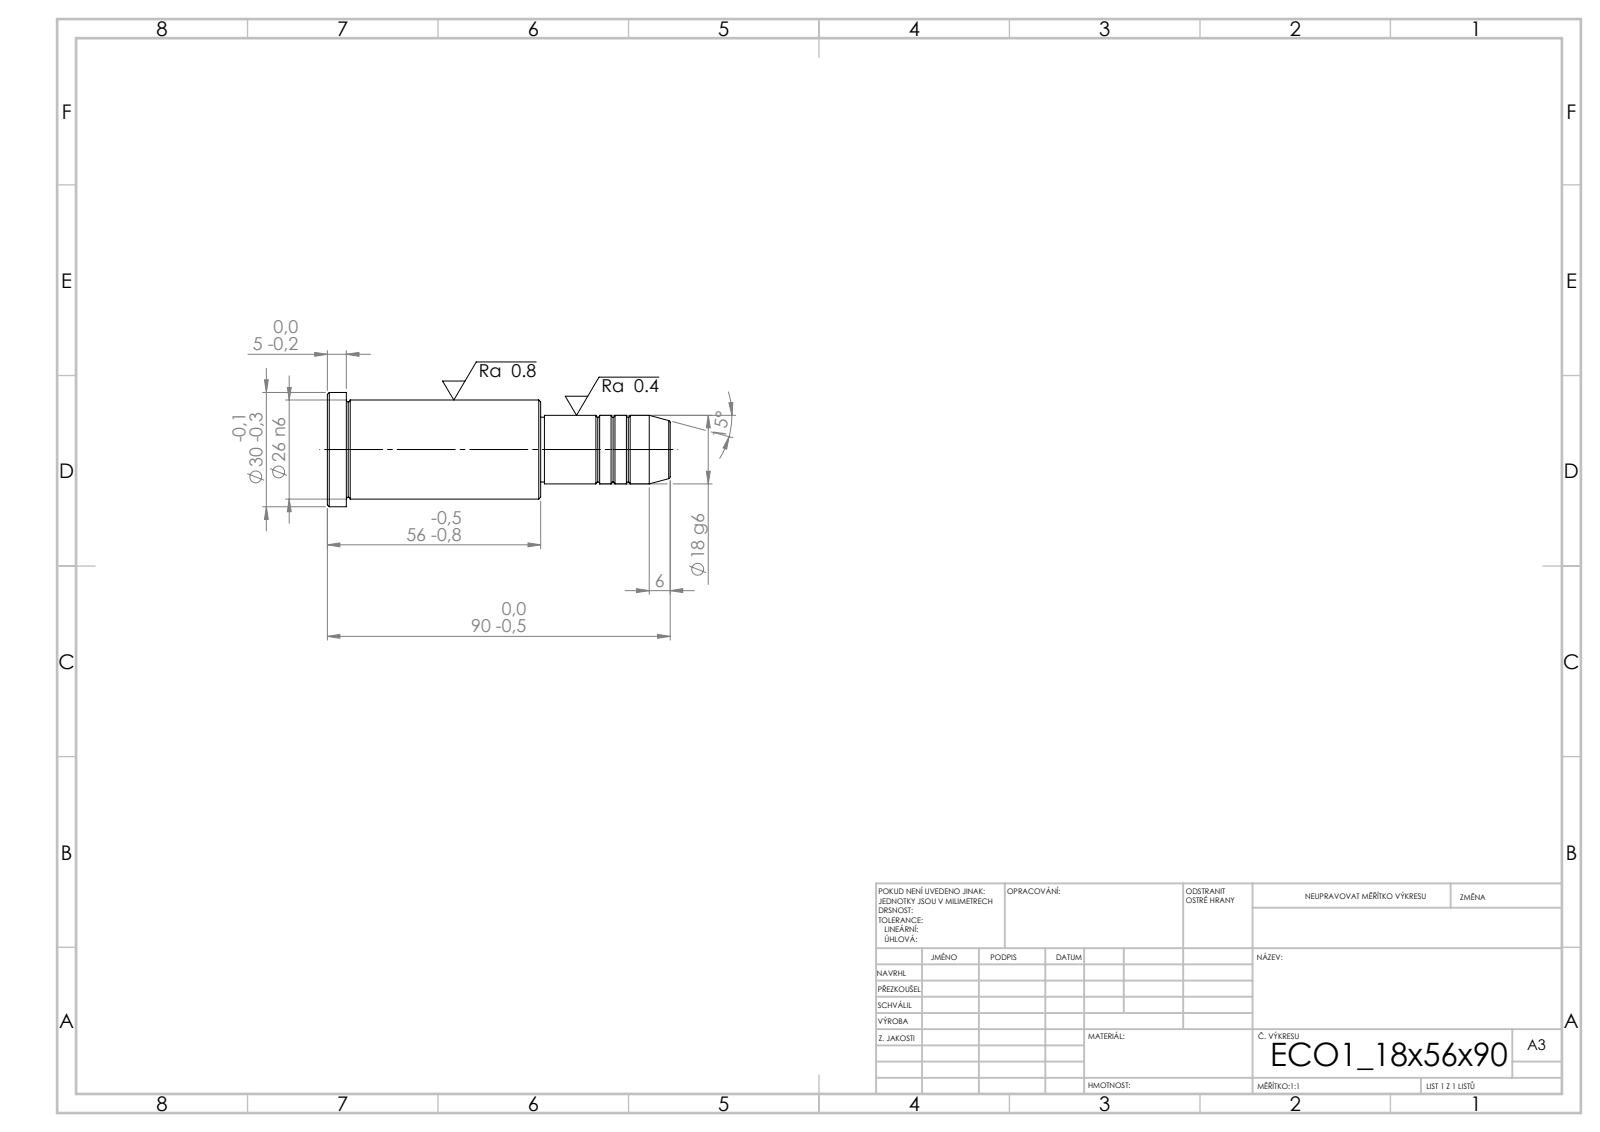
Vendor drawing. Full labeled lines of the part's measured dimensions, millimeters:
STEP written by: SolidWorks 2019 (CONFIG_CONTROL_DESIGN)
Units: millimetres
Bodies: 1 solid, 43 faces (5 planar, 14 cylindrical, 24 other)
Overall size (bounding box): 90 × 30 × 30
Volume: 38 900 mm³ · Surface area: 8 007 mm²
Round bosses / shafts (diameter × count): ⌀30 ×1, ⌀26 ×1, ⌀18 ×1, ⌀17 ×1
Main face-to-face distances: 56, 51, 5, 34, 85, 90, 33, 1, 52, 57
